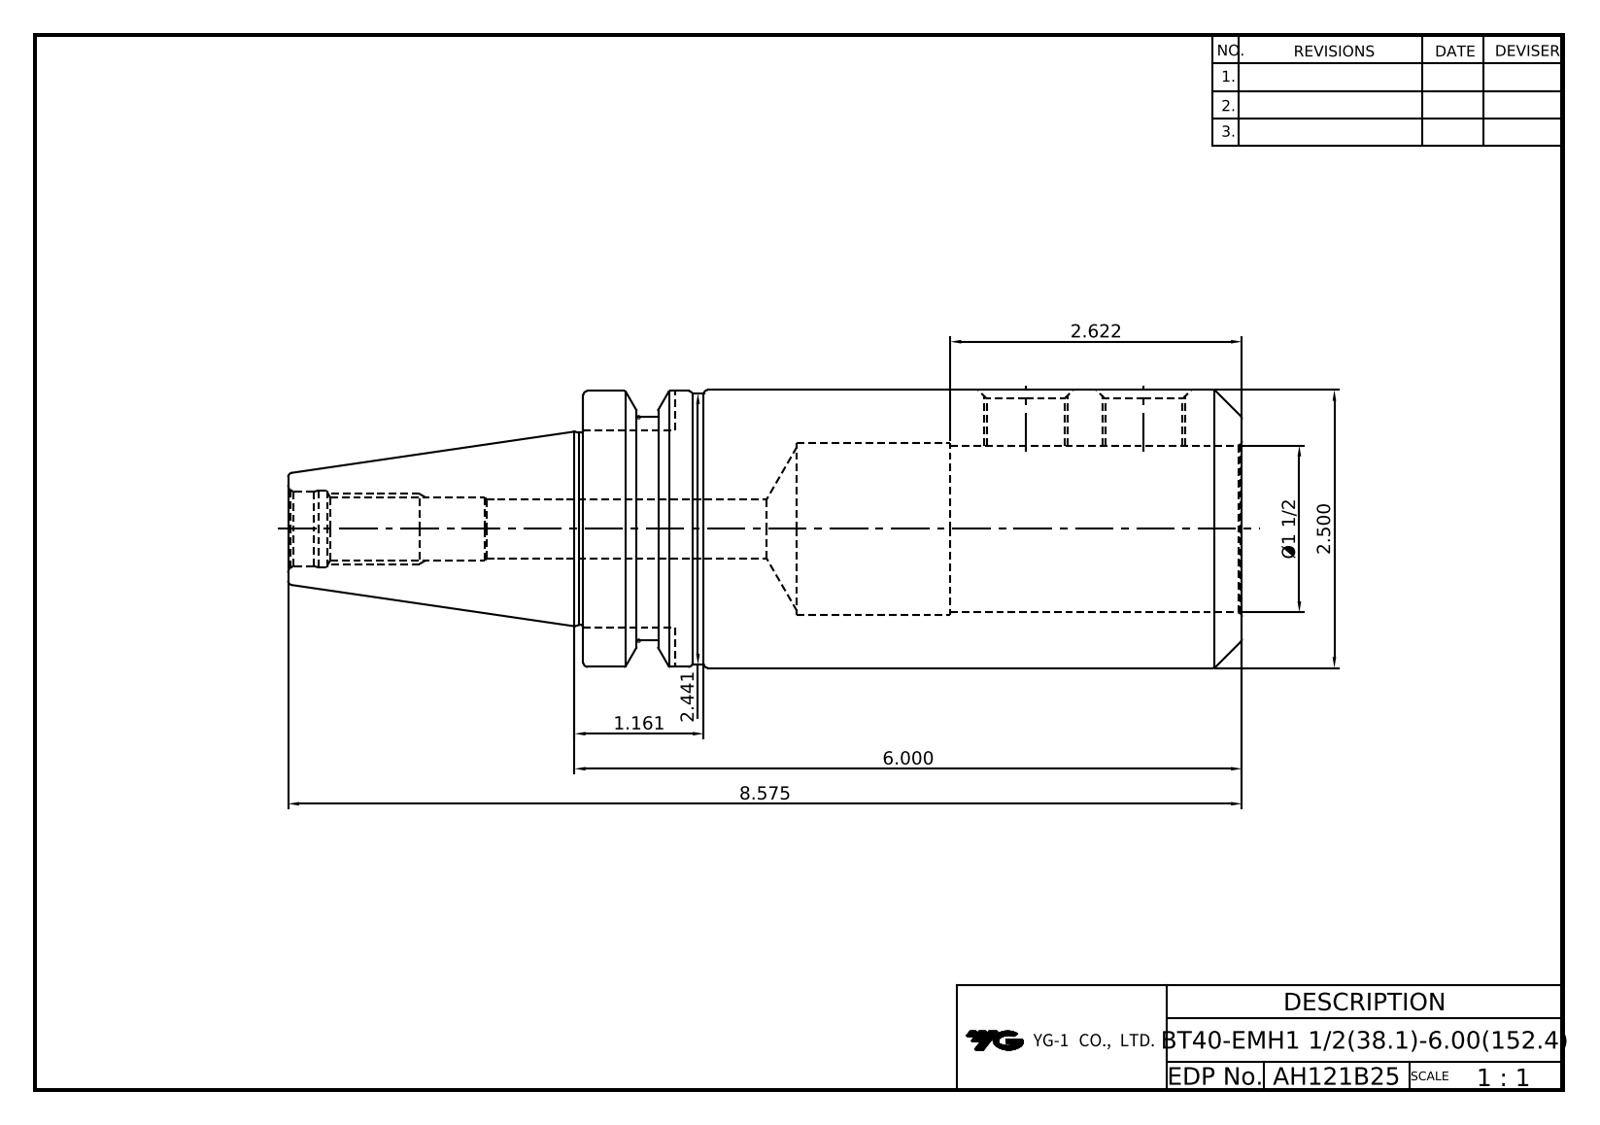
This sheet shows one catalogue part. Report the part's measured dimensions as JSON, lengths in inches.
{"part_name": "LO-BT40-EMH38.1-152.4", "step_written_by": "Autodesk Inventor 2022 (AUTOMOTIVE_DESIGN)", "units": "inches", "bodies": {"solids": 1, "faces": 58, "planar": 16, "cylindrical": 18, "other": 24}, "overall_size": [8.575, 2.5, 2.5], "volume_in3": 23.31, "surface_area_in2": 93.67, "round_holes": [[0.682, 2], [0.531, 1], [0.545, 1], [0.669, 1], [0.693, 1], [1.5, 1], [1.547, 1]], "round_bosses_or_shafts": [[2.5, 1], [2.48, 1], [2.441, 1], [2.071, 1], [1.732, 1]], "partial_cylinders_radius": [[0.317, 1]], "face_to_face_distances": [5.921, 1.78, 0.634, 2.654, 8.575, 3.327, 0.673, 5.248, 4.575, 1.921], "hole_center_spacings": [1.063]}
